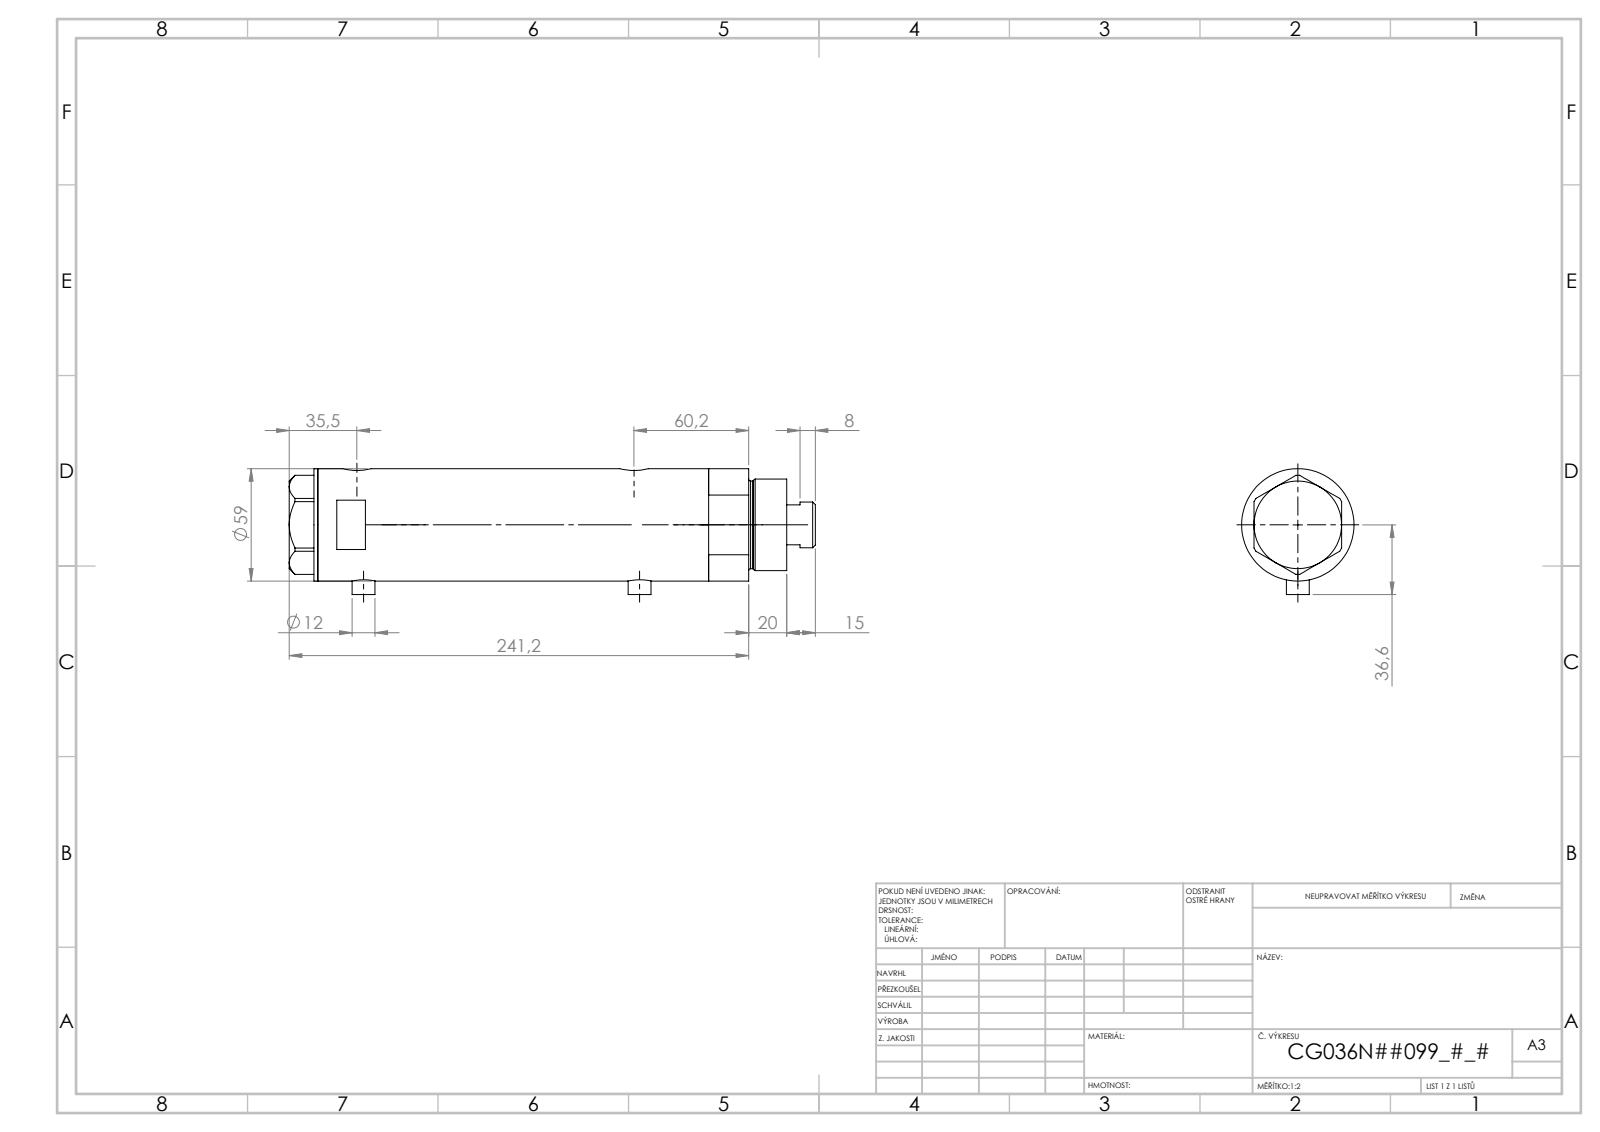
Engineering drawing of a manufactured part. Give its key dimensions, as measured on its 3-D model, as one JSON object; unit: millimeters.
{"part_name": "V270CG_FRONT; V270CG_BACK; V270CG_MIDDLE; V270CG_VC", "step_written_by": "SolidWorks 2019 (CONFIG_CONTROL_DESIGN)", "units": "millimeters", "bodies": {"solids": 4, "faces": 126, "planar": 53, "cylindrical": 53, "other": 20}, "overall_size": [262.42, 60.1, 59], "volume_mm3": 589631, "surface_area_mm2": 119215, "round_holes": [[5, 2], [9.73, 2], [12.5, 2], [15, 2], [8.5, 1], [25, 1], [26.5, 1], [36, 1], [40, 1], [52, 1]], "round_bosses_or_shafts": [[12, 2], [59, 1], [48, 1], [46, 1], [24, 1]], "face_to_face_distances": [156.34, 23.5, 132.84, 15, 38.5, 171.34, 247.42, 232.42, 208.92, 76.08], "hole_center_spacings": [2.9, 3.5, 131.15, 134.05, 134.65, 137.55, 2.89, 2.91]}
